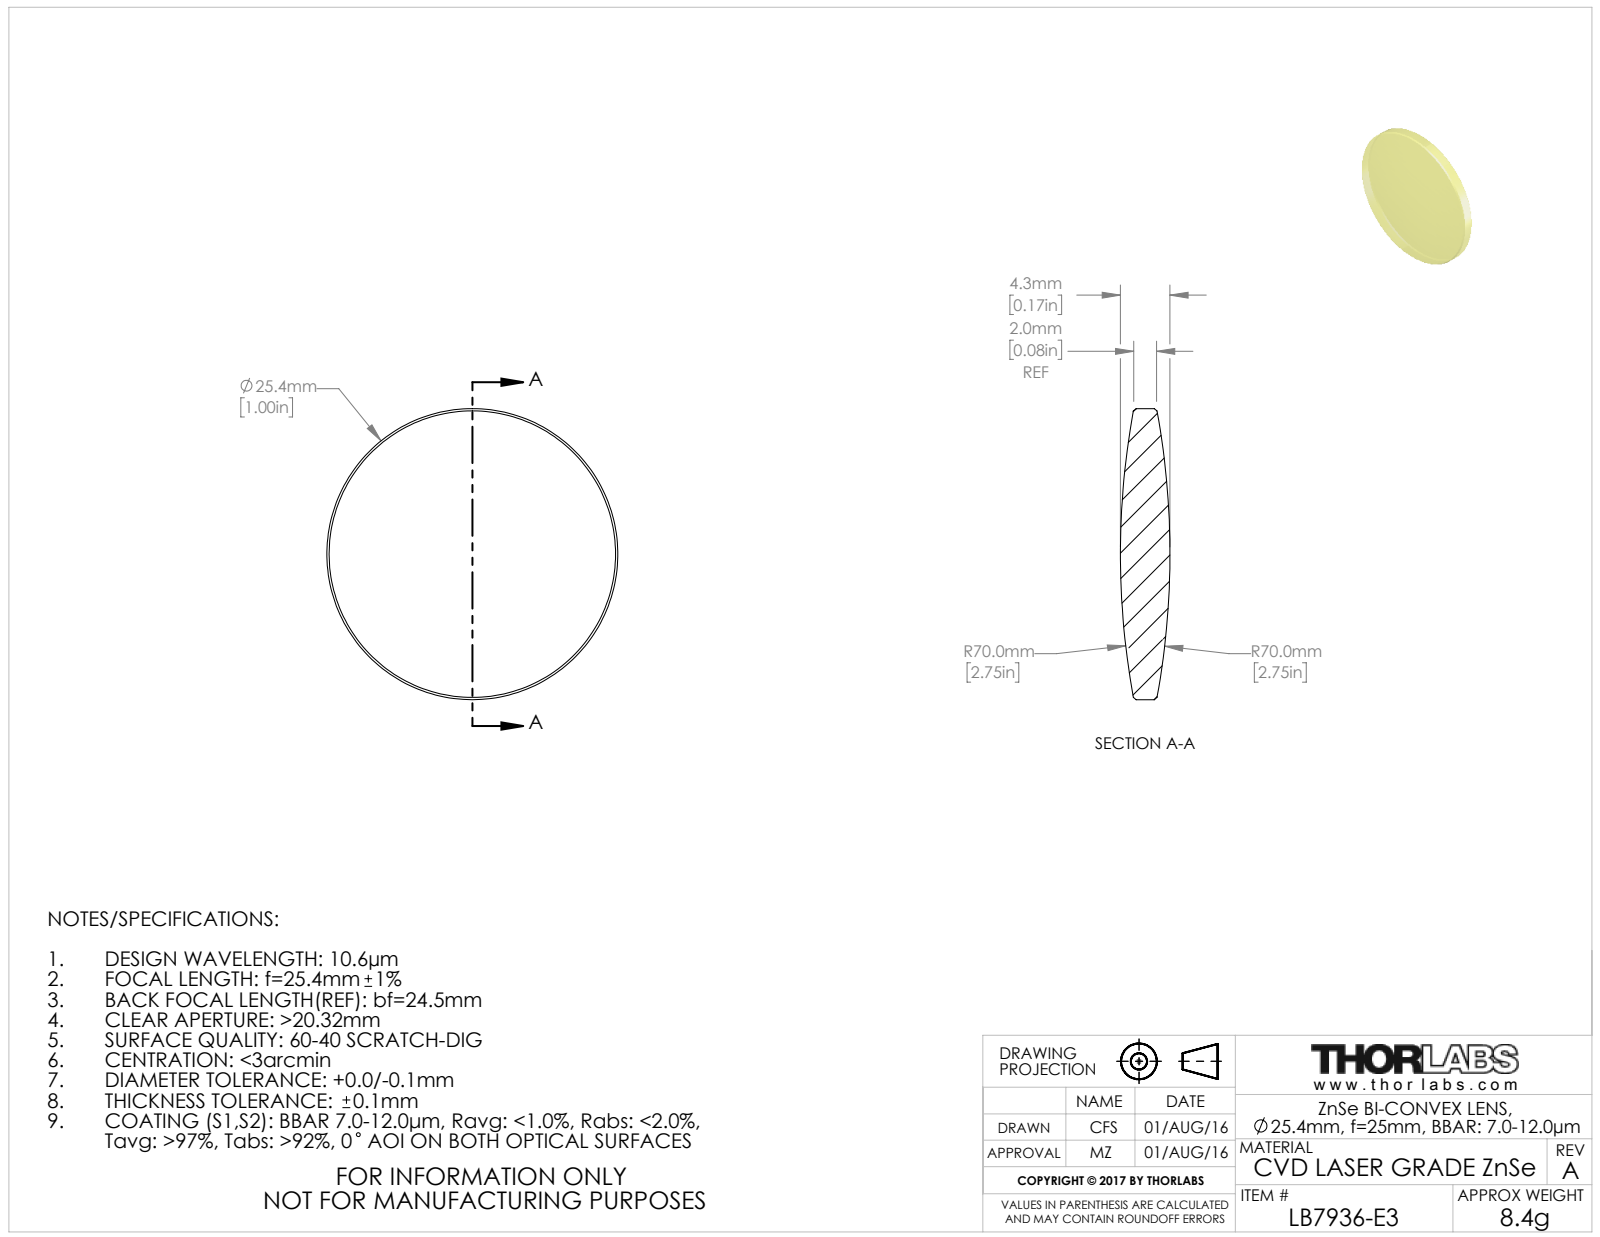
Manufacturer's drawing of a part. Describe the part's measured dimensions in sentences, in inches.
The part is named "TTN051884-E0W". Its 3-D file was written by "SolidWorks 2016 (CONFIG_CONTROL_DESIGN)". It is 1 solid with 10 faces: 0 planar, 2 cylindrical and 8 other. Overall it measures 1 by 1 by 0.17 inches. Its volume is 0.098 cubic inches and its surface area 1.808 square inches. Round bosses or shafts: 1 of diameter 1.
